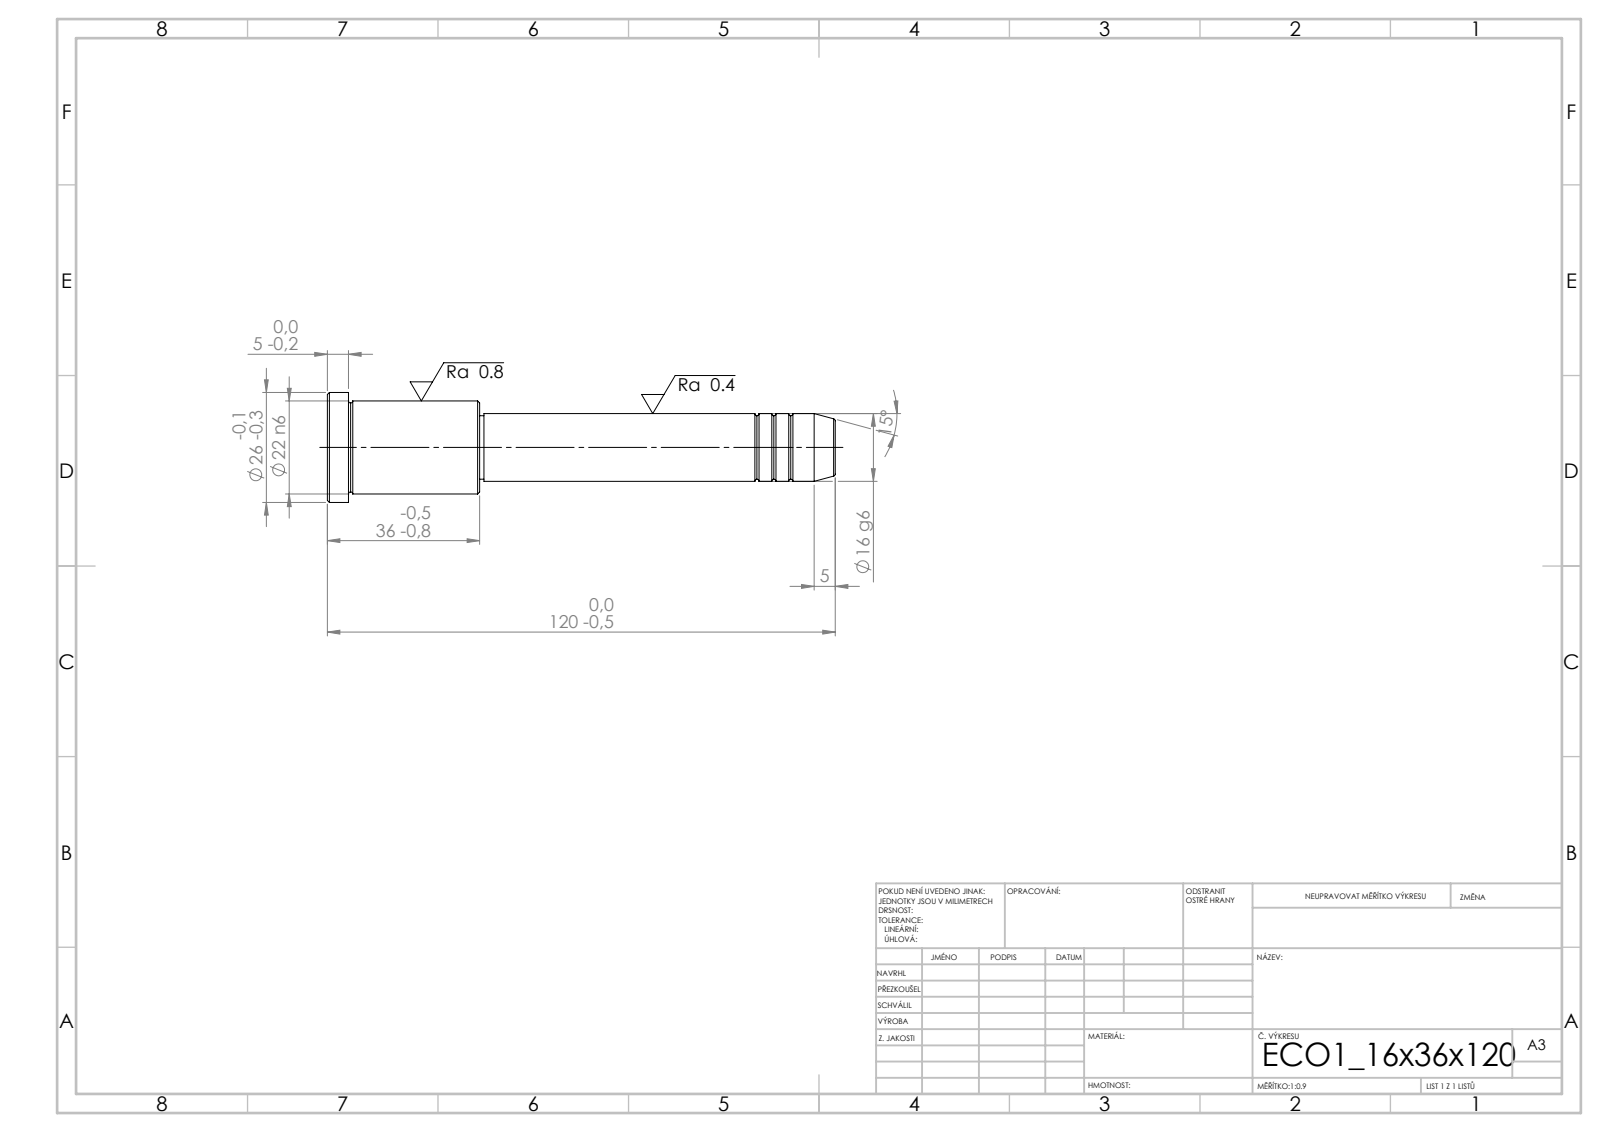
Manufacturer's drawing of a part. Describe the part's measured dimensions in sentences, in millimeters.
Its 3-D file was written by "SolidWorks 2019 (CONFIG_CONTROL_DESIGN)". It is 1 solid with 43 faces: 5 planar, 14 cylindrical and 24 other. Overall it measures 120 by 26 by 26 millimeters. Its volume is 31 041 cubic millimeters and its surface area 7 869 square millimeters. Round bosses or shafts: 1 of diameter 26, 1 of diameter 22, 1 of diameter 16, 1 of diameter 15. The main face-to-face distances are 36, 31, 5, 84, 115, 120, 83, 1, 32, 37.
